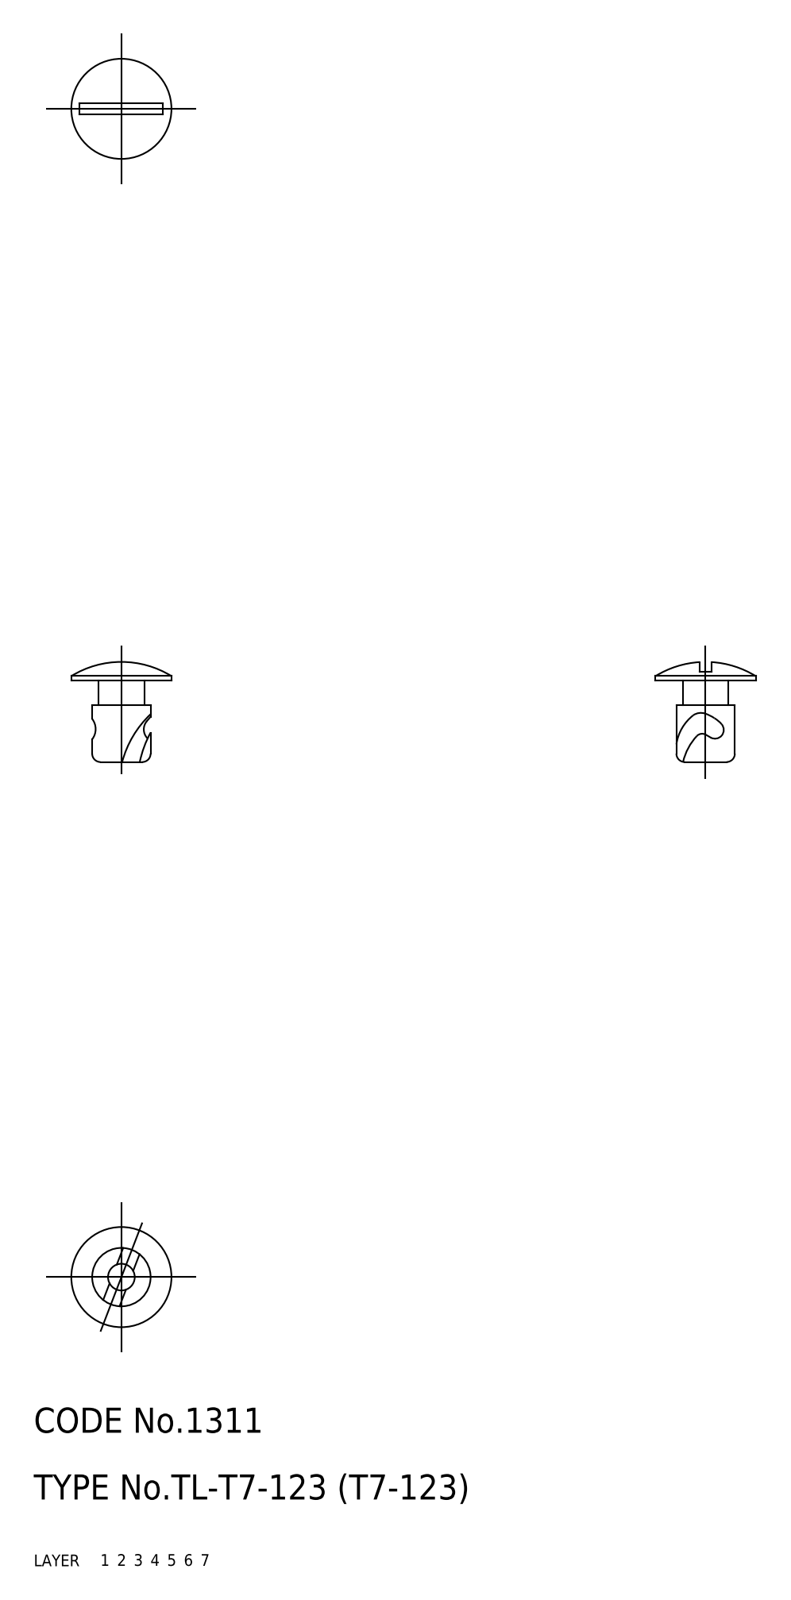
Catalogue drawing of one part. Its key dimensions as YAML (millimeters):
part_name: "fastener"
step_written_by: "CADfix (AUTOMOTIVE_DESIGN)"
units: millimeters
bodies: {solids: 1, faces: 35, planar: 0, cylindrical: 0, other: 35}
overall_size: [12, 12, 11.98]
volume: 362
surface_area: 556
